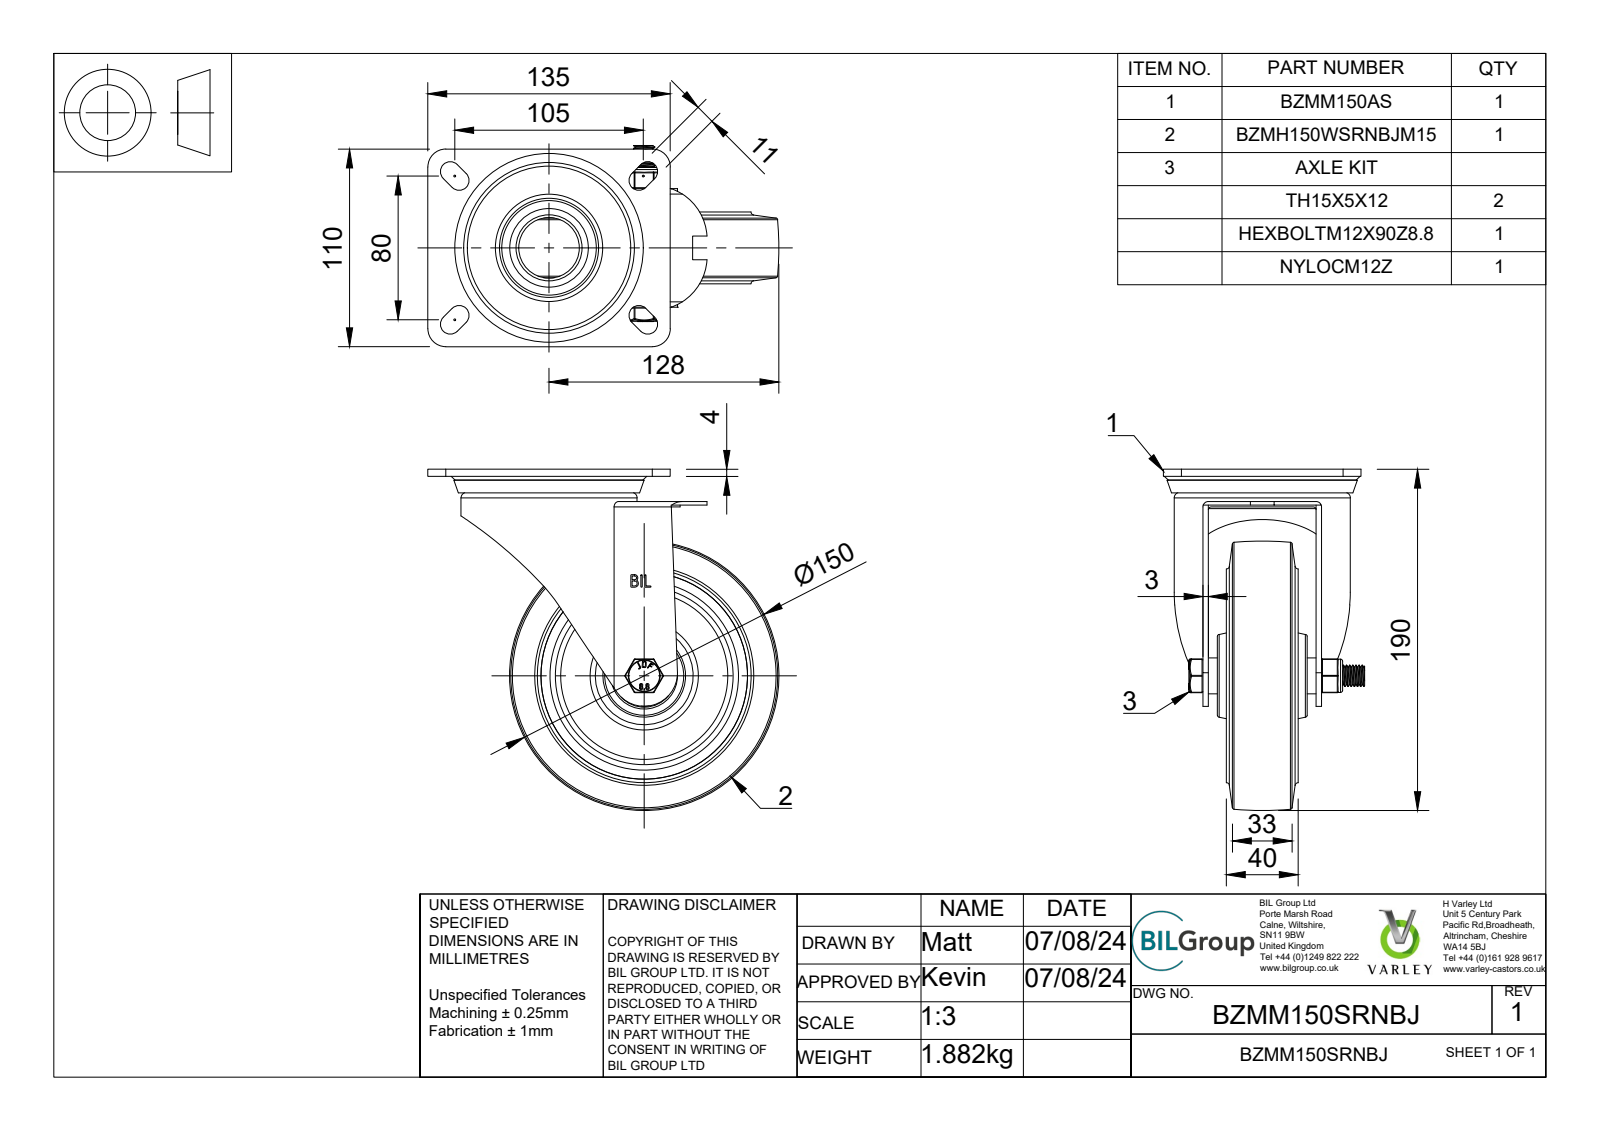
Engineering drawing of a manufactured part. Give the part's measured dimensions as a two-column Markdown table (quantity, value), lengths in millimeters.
| quantity | value |
| --- | --- |
| part name | BZMM150SRNBJ v4; BZMM150AS - 2 v3; ZINC PLATED, PRESSED STEEL TOP PLATE; ZINC PLATED, PRESSED STEEL TOP PLATE Geometry (+7 more) |
| STEP written by | Autodesk Translation Framework v13.14.0.145 (AUTOMOTIVE_DESIGN) |
| units | millimeters |
| bodies | 77 solids, 1104 faces (414 planar, 207 cylindrical, 483 other) |
| overall size | 195.5 × 190 × 112 |
| volume | 635 374 mm³ |
| surface area | 236 224 mm² |
| round holes (diameter × count) | 12 × 1, 12.2 × 1, 12.5 × 1, 14 × 1, 15 × 1, 22.5 × 1, 29 × 1, 30 × 1, 31 × 1, 32 × 1, 33.75 × 1, 35 × 1 |
| round bosses / shafts (diameter × count) | 98 × 1, 78 × 1, 50 × 1, 30.5 × 1, 23 × 1, 20 × 1, 18.5 × 1, 18 × 1 |
| partial cylindrical surfaces (radius × count) | 0.5 × 20, 5.5 × 8, 0.47 × 4, 0.9 × 4, 1.5 × 4, 10 × 4, 0.89 × 2, 0.89 × 2 |
| main face-to-face distances | 5, 3, 9, 4, 13, 27.5, 30.5, 32.5, 16, 35.5 |
